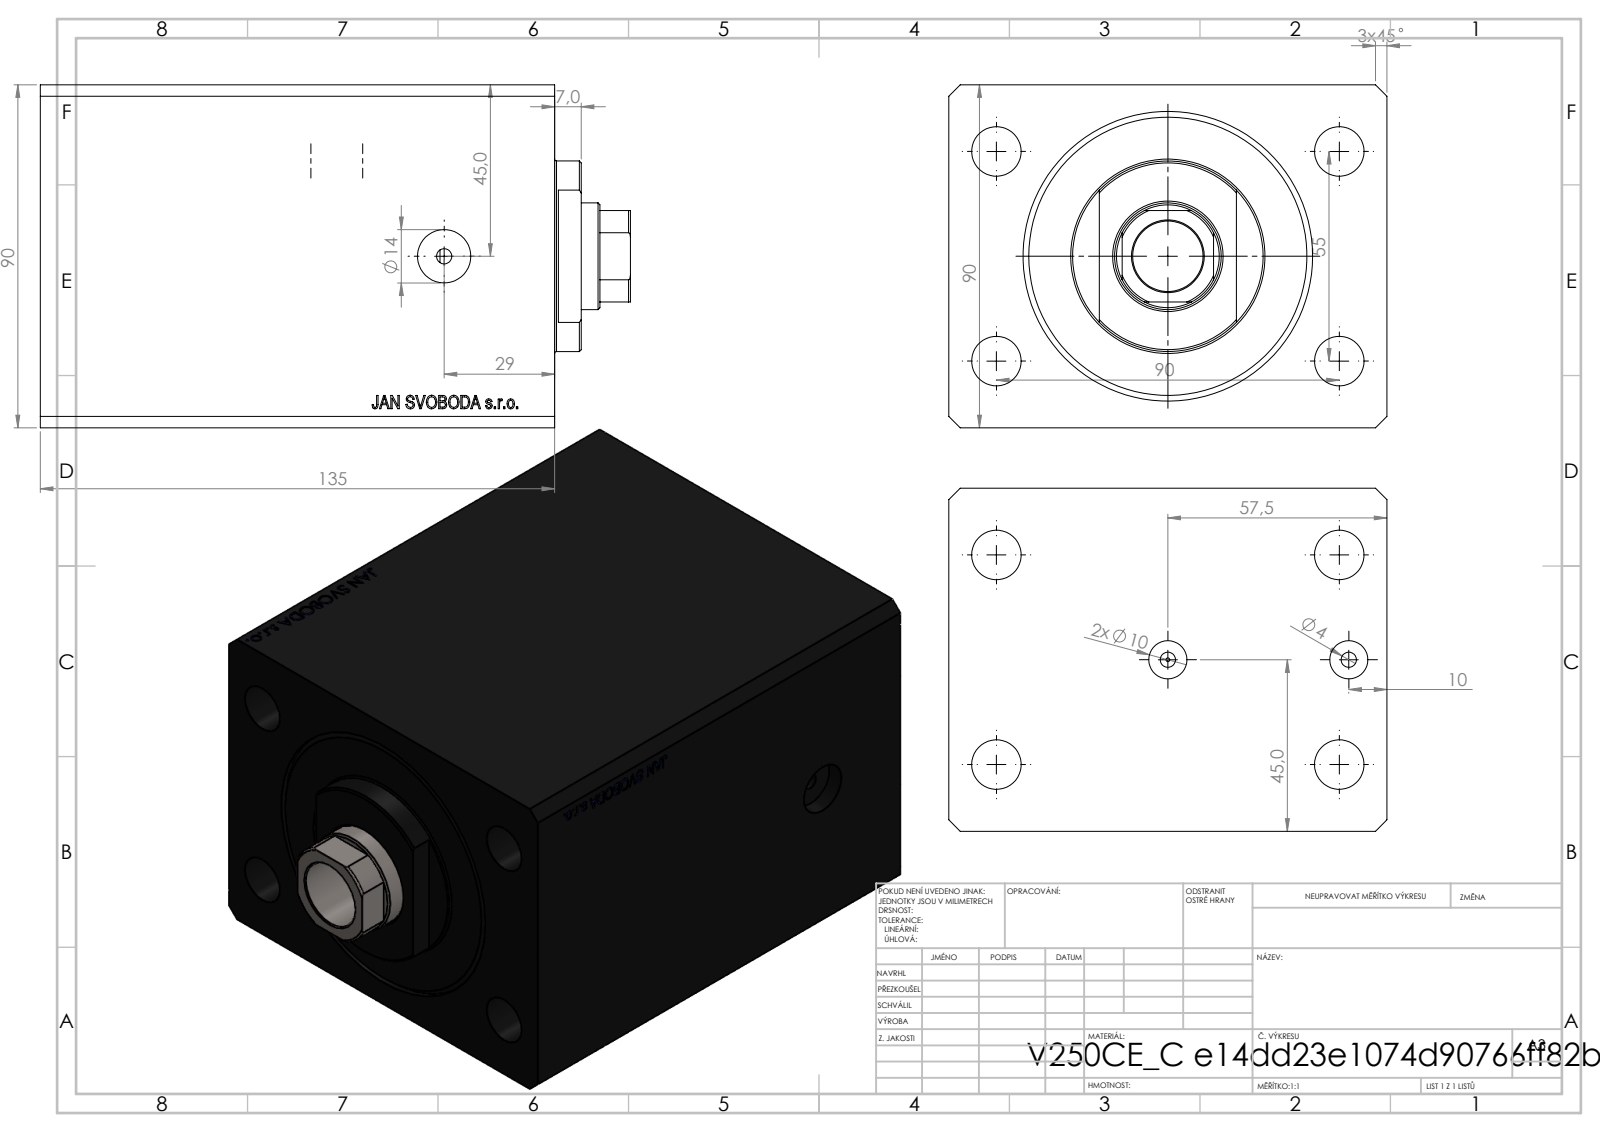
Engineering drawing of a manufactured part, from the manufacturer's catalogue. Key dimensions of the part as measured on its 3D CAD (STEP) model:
Part name (STEP PRODUCT): V250CE_C_Body; V250CE_C_VCP; V250CE_VC_C
STEP written by: SolidWorks 2019 (CONFIG_CONTROL_DESIGN)
Units: millimetres
Bodies: 3 solids, 868 faces (428 planar, 46 cylindrical, 394 other)
Overall size (bounding box): 154.9 × 115 × 90
Volume: 1 204 000 mm³ · Surface area: 166 515 mm²
Round holes (diameter × count): ⌀4 ×4, ⌀13 ×4, ⌀10 ×2, ⌀14 ×2, ⌀1.25 ×1, ⌀18.5 ×1, ⌀28 ×1, ⌀63 ×1, ⌀76 ×1
Round bosses / shafts (diameter × count): ⌀50 ×1
Partial cylindrical surfaces — rounded edges, fillets, slot ends (radius × count): R13.5 ×1
Main face-to-face distances: 90, 115, 135, 17.9, 117.1, 104.9, 87, 30.1, 50, 54.9
Hole centre spacings: 52.74, 27.61, 55, 90, 96.5, 105.48, 47.5, 77
